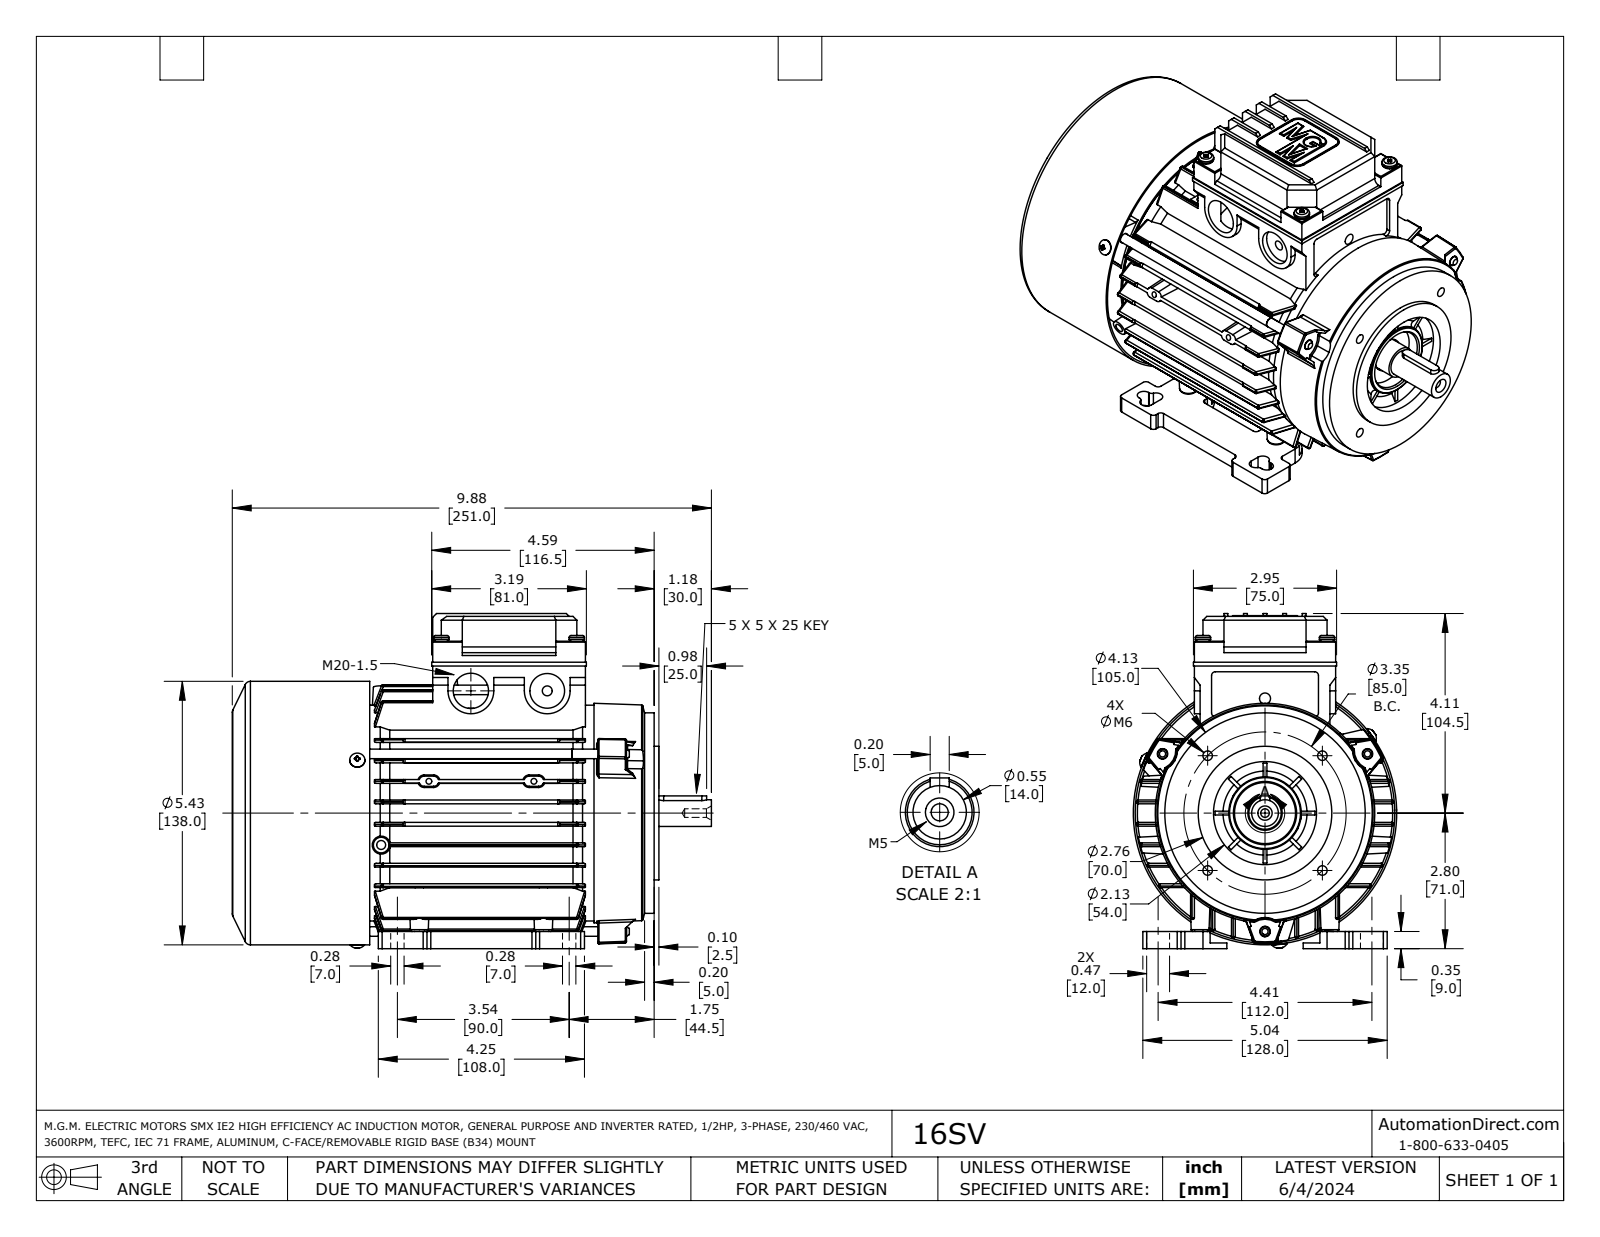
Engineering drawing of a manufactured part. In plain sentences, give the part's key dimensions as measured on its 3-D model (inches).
The part is named "16SV". Its 3-D file was written by "SolidWorks 2021 (AUTOMOTIVE_DESIGN)". It is 27 solids with 3702 faces: 1133 planar, 1479 cylindrical and 1090 other. Overall it measures 9.882 by 6.909 by 5.433 inches. Its volume is 35.18 cubic inches and its surface area 688.7 square inches. Round holes: 14 of diameter 0.118, 7 of diameter 0.13, 7 of diameter 0.217, 4 of diameter 0.157, 4 of diameter 0.177, 4 of diameter 0.197, 4 of diameter 0.236, 4 of diameter 0.256, 4 of diameter 0.394, 3 of diameter 0.126, 3 of diameter 0.276, 2 of diameter 0.185. Round bosses or shafts: 10 of diameter 0.118, 7 of diameter 0.315, 7 of diameter 0.197, 4 of diameter 0.386, 4 of diameter 0.138, 3 of diameter 0.079, 1 of diameter 5.433, 1 of diameter 4.449. Partial cylindrical surfaces (rounded edges, fillets, slot ends): 252 of radius 0.039, 60 of radius 0.035, 56 of radius 0.008, 38 of radius 0.079, 36 of radius 0.016, 30 of radius 0.02, 16 of radius 0.004, 16 of radius 0.033. The main face-to-face distances are 0.079, 0.422, 0.843, 1.726, 0.343, 2.148, 2.57, 0.5, 1.305, 1.805. The hole center spacings are 0.478, 2.535, 0.571, 0.748, 1.102, 1.22, 1.222, 1.559.
